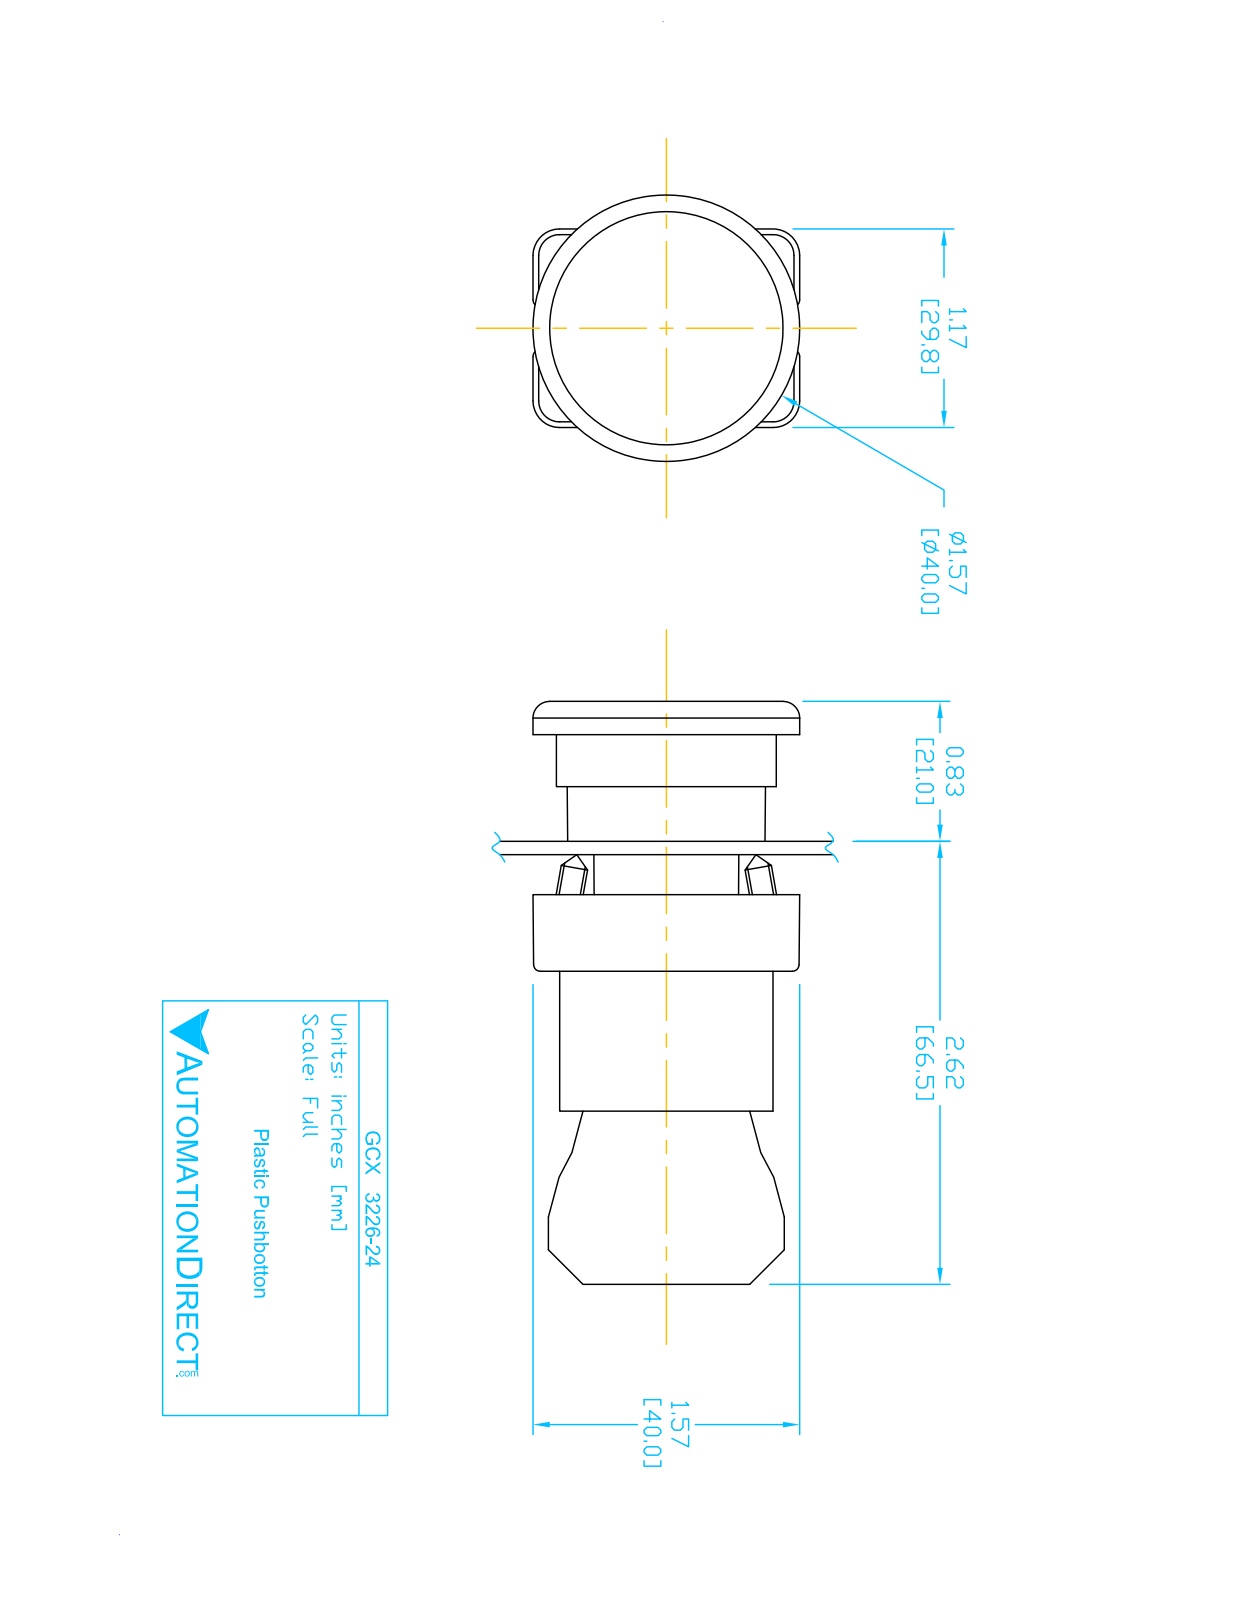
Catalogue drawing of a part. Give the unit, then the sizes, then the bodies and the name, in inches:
Units: inches
Overall size (bounding box): 3.469 × 1.581 × 1.575
Round holes (diameter × count): ⌀0.079 ×2, ⌀0.124 ×2, ⌀0.13 ×2, ⌀0.087 ×1, ⌀0.197 ×1, ⌀0.469 ×1, ⌀0.878 ×1, ⌀0.888 ×1, ⌀1.024 ×1, ⌀1.181 ×1
Round bosses / shafts (diameter × count): ⌀0.157 ×4, ⌀1.299 ×1, ⌀1.175 ×1, ⌀0.945 ×1, ⌀0.856 ×1, ⌀0.78 ×1, ⌀0.504 ×1
Partial cylindrical surfaces — rounded edges, fillets, slot ends (radius × count): R0.059 ×24, R0.041 ×12, R0.124 ×12, R0.157 ×12, R0.039 ×8, R0.128 ×2, R0.02 ×1, R0.063 ×1
Main face-to-face distances: 0.827, 2.445, 1.618, 0.579, 2.287, 1.461, 0.157, 0.587, 0.031, 1.165
Hole centre spacings: 0.236, 0.539, 0.472, 0.484
Volume: 2.895 in³ · Surface area: 40.89 in²
Bodies: 7 solids, 431 faces (252 planar, 146 cylindrical, 33 other)
Part name (STEP PRODUCT): GCX3226-24; ECX3029-2; ecx1030; ECX1050 (+1 more)
STEP written by: SolidWorks 2016 (AUTOMOTIVE_DESIGN)
